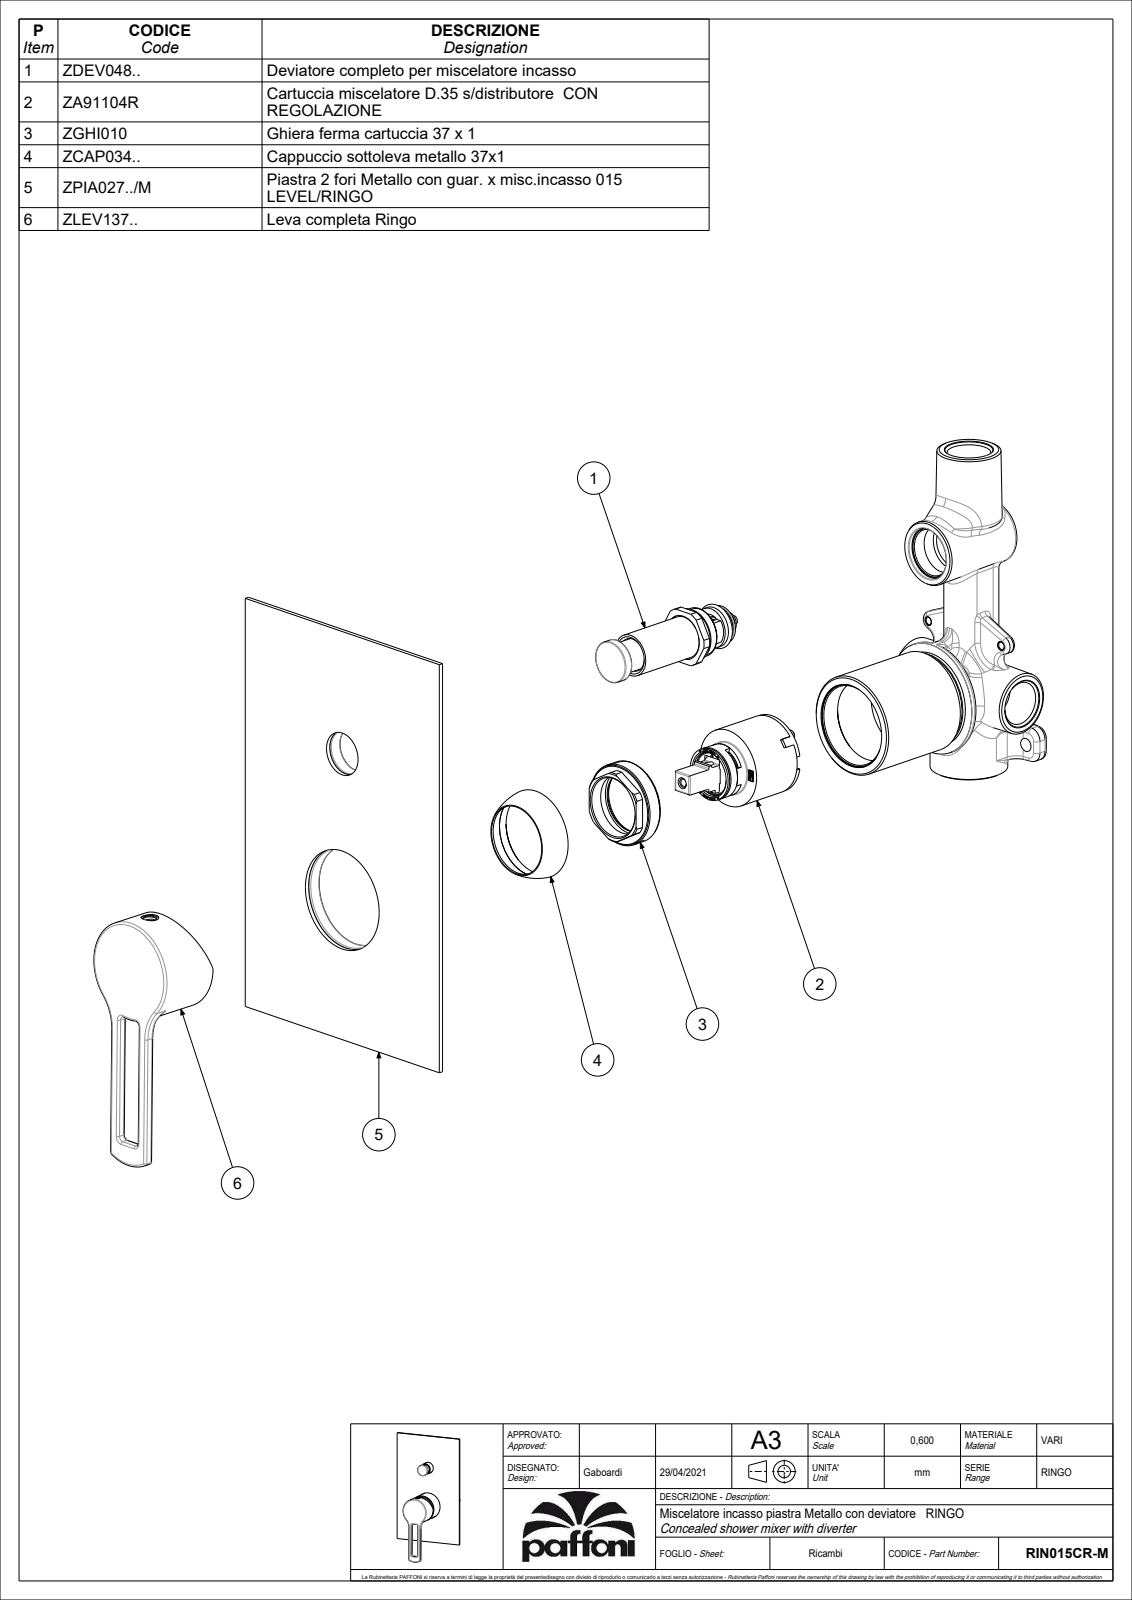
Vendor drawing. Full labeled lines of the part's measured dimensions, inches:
Part name (STEP PRODUCT): RIN015CR-M
STEP written by: CREO PARAMETRIC BY PTC INC, 2020044 (CONFIG_CONTROL_DESIGN)
Units: inches
Bodies: 5 solids, 1047 faces (586 planar, 251 cylindrical, 210 other)
Overall size (bounding box): 8.465 × 4.724 × 2.325
Volume: 5.602 in³ · Surface area: 131.5 in²
Round holes (diameter × count): ⌀0.157 ×2, ⌀0.768 ×2, ⌀0.118 ×1, ⌀0.13 ×1, ⌀0.197 ×1, ⌀0.307 ×1, ⌀0.413 ×1, ⌀0.583 ×1, ⌀0.783 ×1, ⌀1.055 ×1, ⌀1.142 ×1, ⌀1.22 ×1
Round bosses / shafts (diameter × count): ⌀1.764 ×1, ⌀1.378 ×1, ⌀1.268 ×1, ⌀0.925 ×1, ⌀0.921 ×1, ⌀0.858 ×1, ⌀0.736 ×1, ⌀0.732 ×1
Partial cylindrical surfaces — rounded edges, fillets, slot ends (radius × count): R0.02 ×35, R0.039 ×14, R0.006 ×11, R0.012 ×4, R0.079 ×4, R0.787 ×2, R0.276 ×1, R0.366 ×1
Main face-to-face distances: 0.079, 0.039, 2.315, 2.236, 2.138, 2.098, 0.177, 0.059, 0.138, 2.276
Hole centre spacings: 0.433, 2.677
